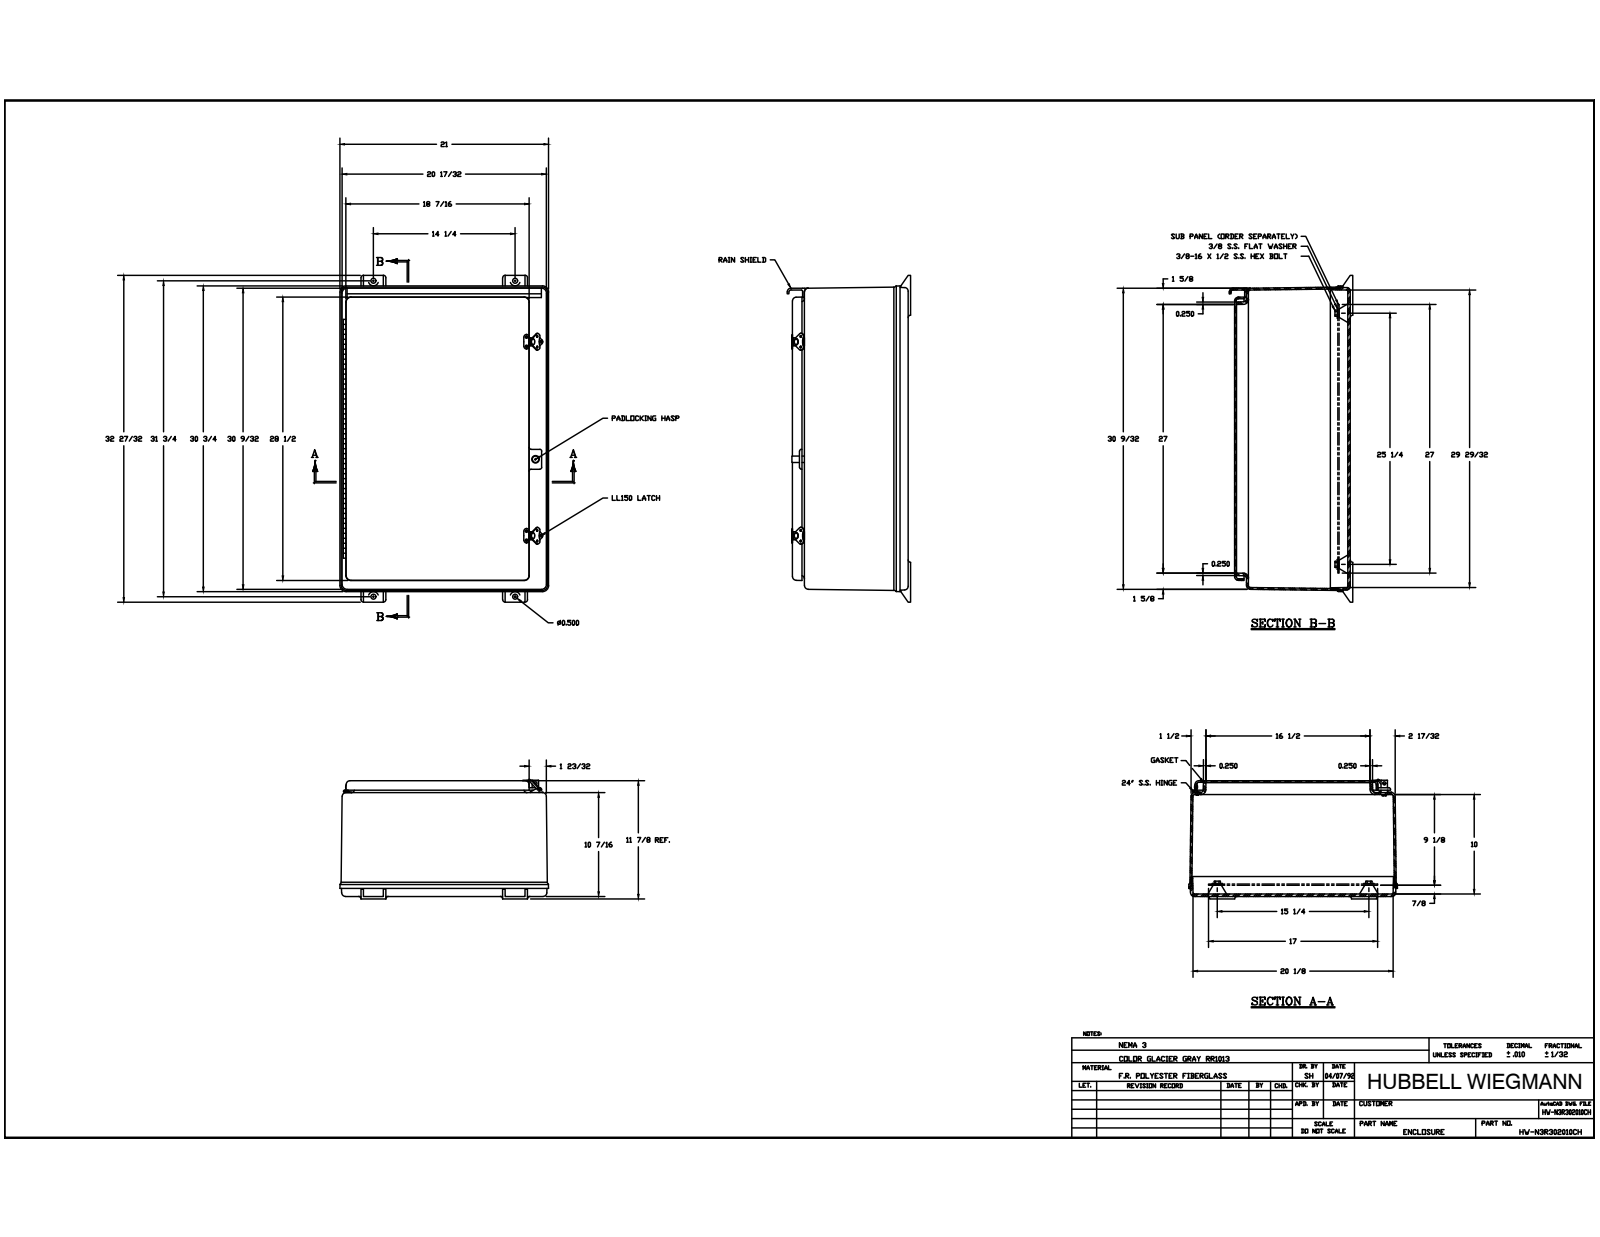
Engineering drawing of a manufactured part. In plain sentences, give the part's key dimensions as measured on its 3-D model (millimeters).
The part is named "WPN302010SRT; WPN3020B; N3020RS; 0.13 RIVET PIN (+8 more)". Its 3-D file was written by "Autodesk Inventor 2014 (AUTOMOTIVE_DESIGN)". It is 40 solids with 1210 faces: 486 planar, 476 cylindrical and 248 other. Overall it measures 834.23 by 533.4 by 315.91 millimeters. Its volume is 8 685 000 cubic millimeters and its surface area 3 620 000 square millimeters. Round holes: 26 of diameter 3.3, 11 of diameter 1.65, 8 of diameter 1.59, 4 of diameter 3.5, 4 of diameter 4.76, 4 of diameter 14.3, 2 of diameter 12.95, 2 of diameter 12.96, 1 of diameter 3.17, 1 of diameter 3.43, 1 of diameter 3.97, 1 of diameter 5.11. Round bosses or shafts: 11 of diameter 7.54, 8 of diameter 3.56, 2 of diameter 12.7, 1 of diameter 6.35, 1 of diameter 5.11, 1 of diameter 5.08. Partial cylindrical surfaces (rounded edges, fillets, slot ends): 60 of radius 0.25, 24 of radius 6.35, 22 of radius 4.76, 14 of radius 7.94, 12 of radius 9.53, 12 of radius 12.7, 8 of radius 0.76, 7 of radius 3.17. The main face-to-face distances are 4.76, 6.35, 3.96, 295.27, 288.92, 291.31, 284.96, 30.16, 265.11, 260.35. The hole center spacings are 495.3, 23.82, 39.16, 190.5, 393.7, 21.79, 21.8, 167.95.
